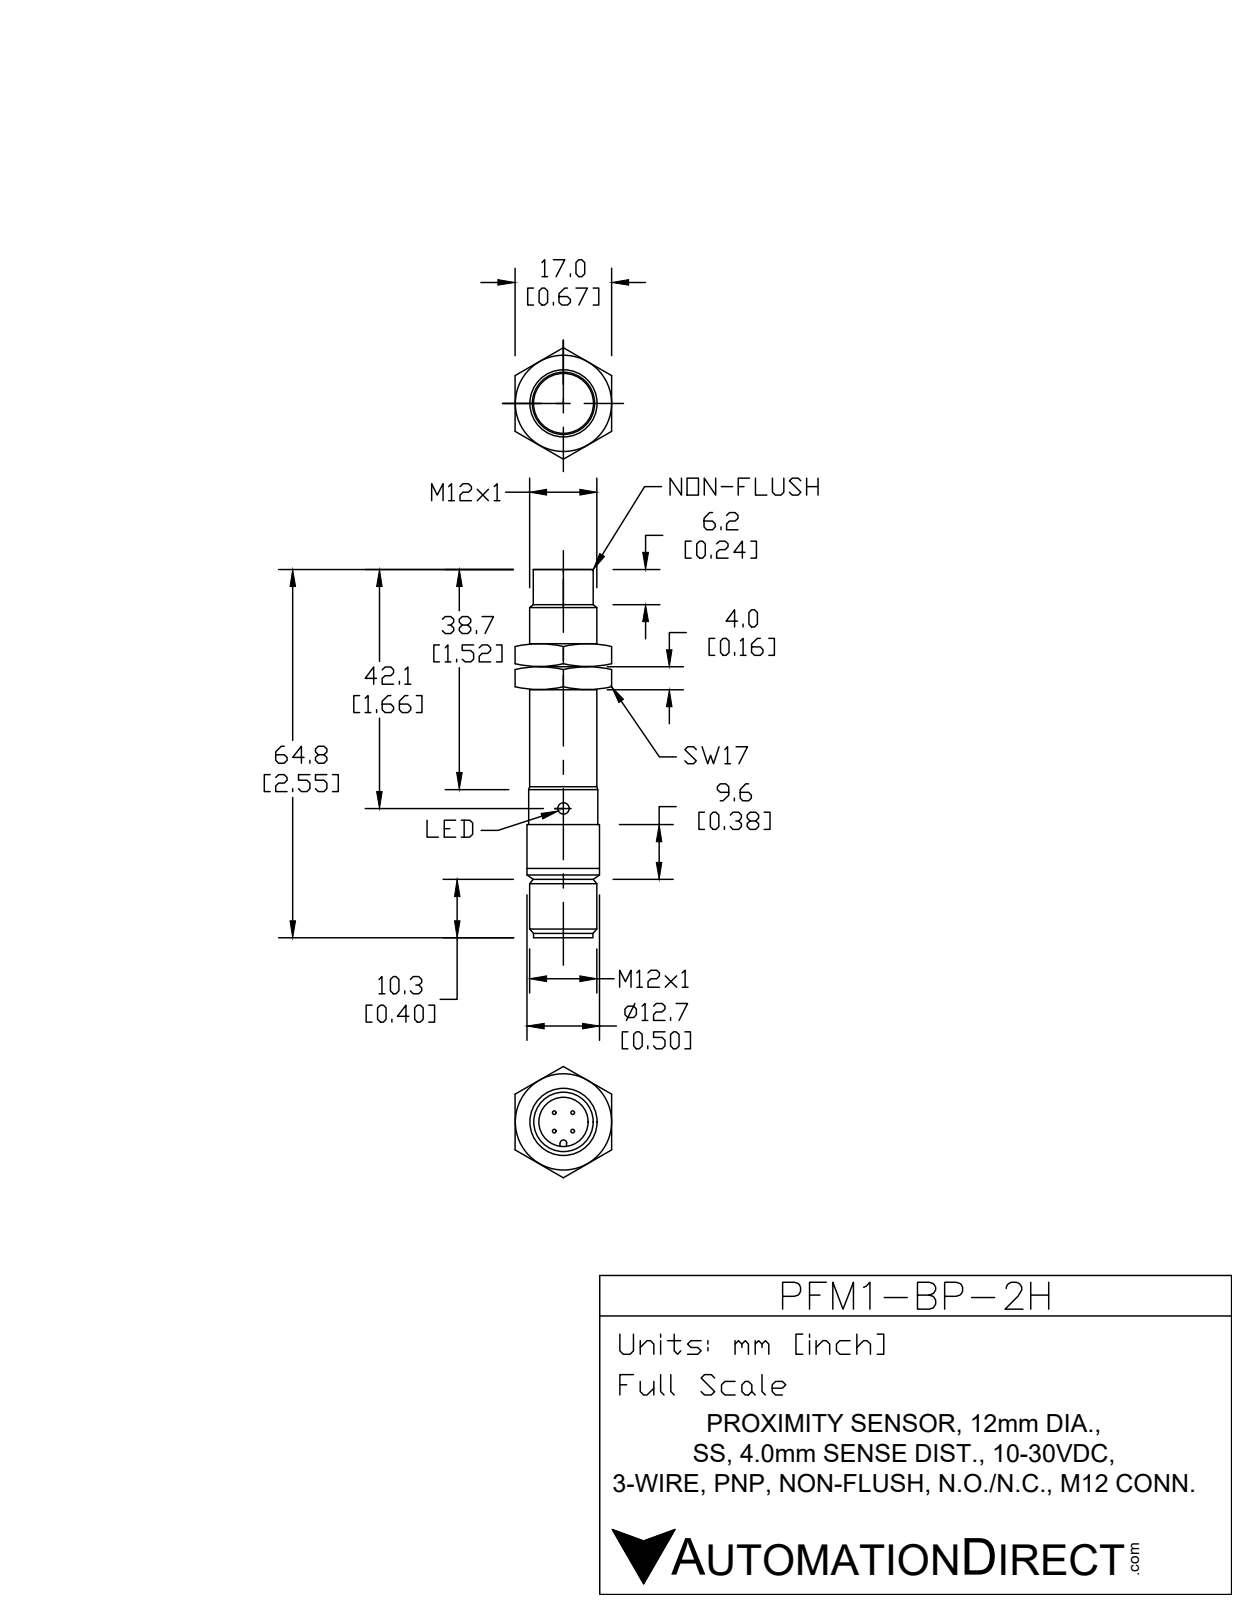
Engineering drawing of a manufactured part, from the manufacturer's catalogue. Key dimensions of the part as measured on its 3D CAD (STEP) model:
Part name (STEP PRODUCT): PFM1-BP-2H
STEP written by: SolidWorks 2017 (AUTOMOTIVE_DESIGN)
Units: inches
Bodies: 4 solids, 73 faces (11 planar, 36 cylindrical, 26 other)
Overall size (bounding box): 2.543 × 0.5 × 0.5
Volume: 0.409 in³ · Surface area: 6.284 in²
Round holes (diameter × count): ⌀0.118 ×1, ⌀0.331 ×1, ⌀0.335 ×1, ⌀0.374 ×1
Round bosses / shafts (diameter × count): ⌀0.039 ×4, ⌀0.5 ×1, ⌀0.472 ×1, ⌀0.413 ×1, ⌀0.394 ×1, ⌀0.37 ×1
Partial cylindrical surfaces — rounded edges, fillets, slot ends (radius × count): R0.024 ×1, R0.219 ×1
Main face-to-face distances: 1.839, 1.909, 0.071, 0.236, 2.075, 2.146, 2.193, 1.957, 0.118, 0.047
